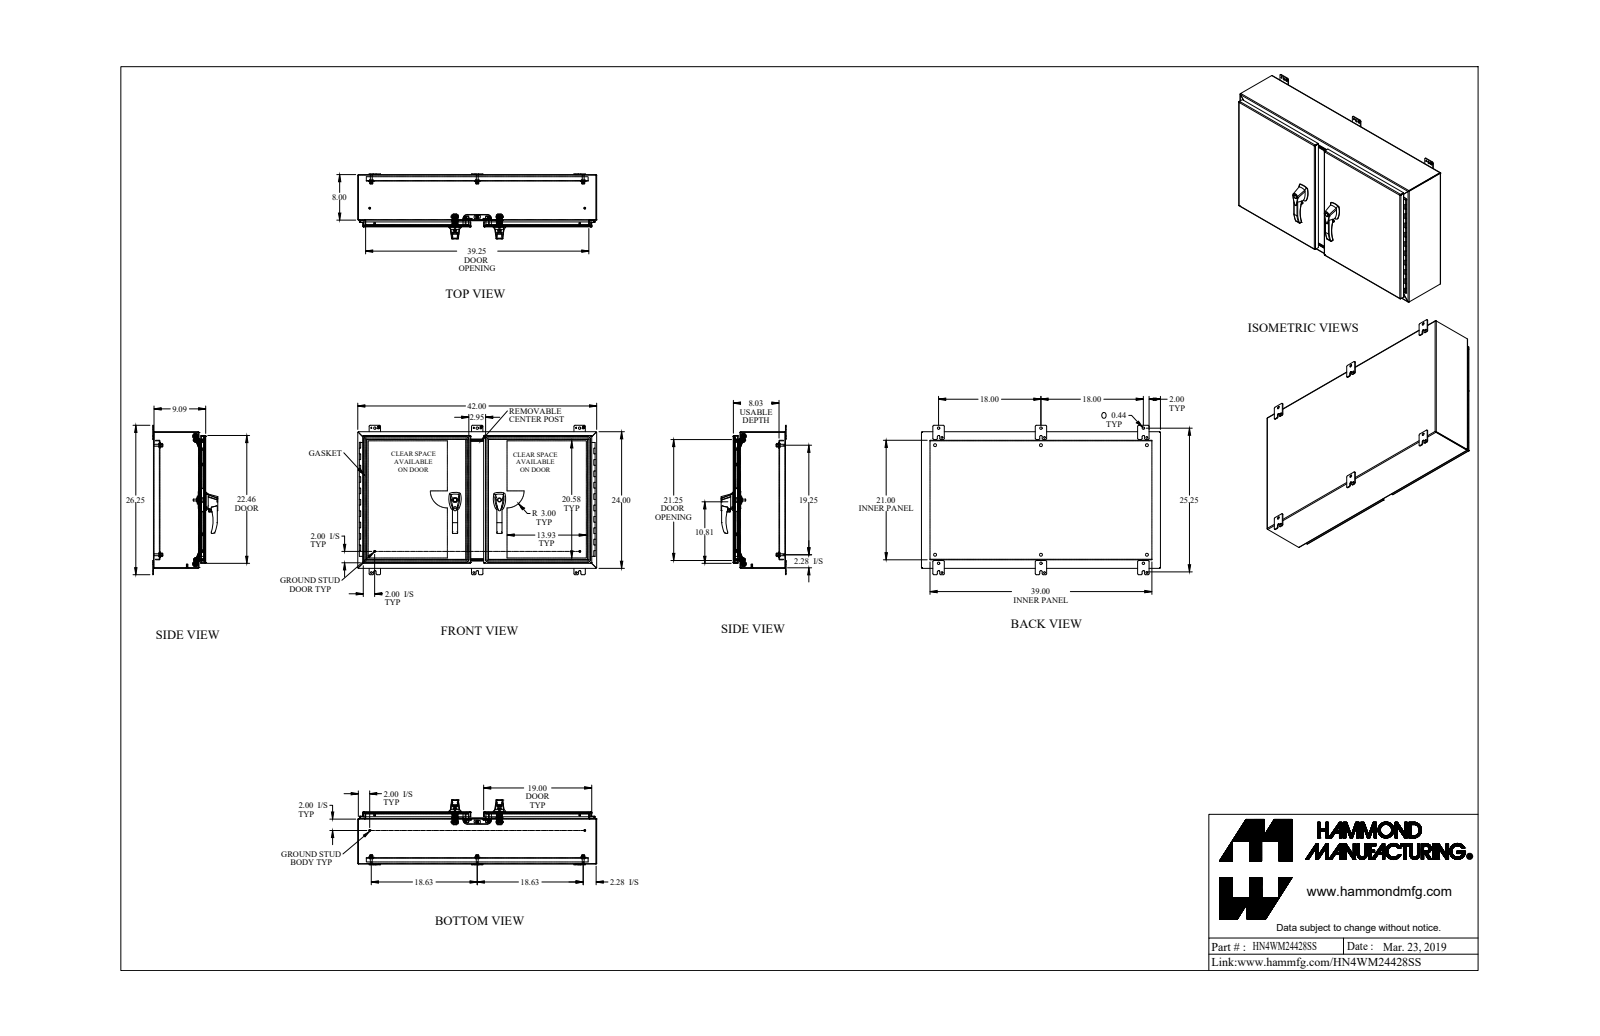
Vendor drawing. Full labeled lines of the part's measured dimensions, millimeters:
Part name (STEP PRODUCT): HN4WM24428SS
STEP written by: SolidWorks 2018 (AUTOMOTIVE_DESIGN)
Units: millimetres
Bodies: 108 solids, 2624 faces (1243 planar, 1101 cylindrical, 280 other)
Overall size (bounding box): 1066.8 × 666.8 × 290.2
Volume: 7 879 000 mm³ · Surface area: 6 365 000 mm²
Round holes (diameter × count): ⌀6.4 ×10, ⌀8 ×9, ⌀7.7 ×8, ⌀5.1 ×6, ⌀7.8 ×6, ⌀11.3 ×6, ⌀12.7 ×6, ⌀6.5 ×4, ⌀7.1 ×4, ⌀7.1 ×4, ⌀8 ×4, ⌀9.9 ×4
Round bosses / shafts (diameter × count): ⌀25.4 ×10, ⌀16.5 ×6, ⌀9.5 ×6, ⌀8.4 ×6, ⌀7.4 ×6, ⌀19.1 ×4, ⌀16 ×4, ⌀15.9 ×4
Partial cylindrical surfaces — rounded edges, fillets, slot ends (radius × count): R3.2 ×37, R0.5 ×32, R4.8 ×27, R6.4 ×26, R1.5 ×22, R12.7 ×21, R1.2 ×19, R3.6 ×19
Main face-to-face distances: 2.4, 26.2, 2.4, 230.9, 228.5, 23.8, 233.3, 230.9, 28.6, 202.3
Hole centre spacings: 198.5, 152.4, 1030.9, 28.6, 32.7, 51.8, 184.8, 200.5
